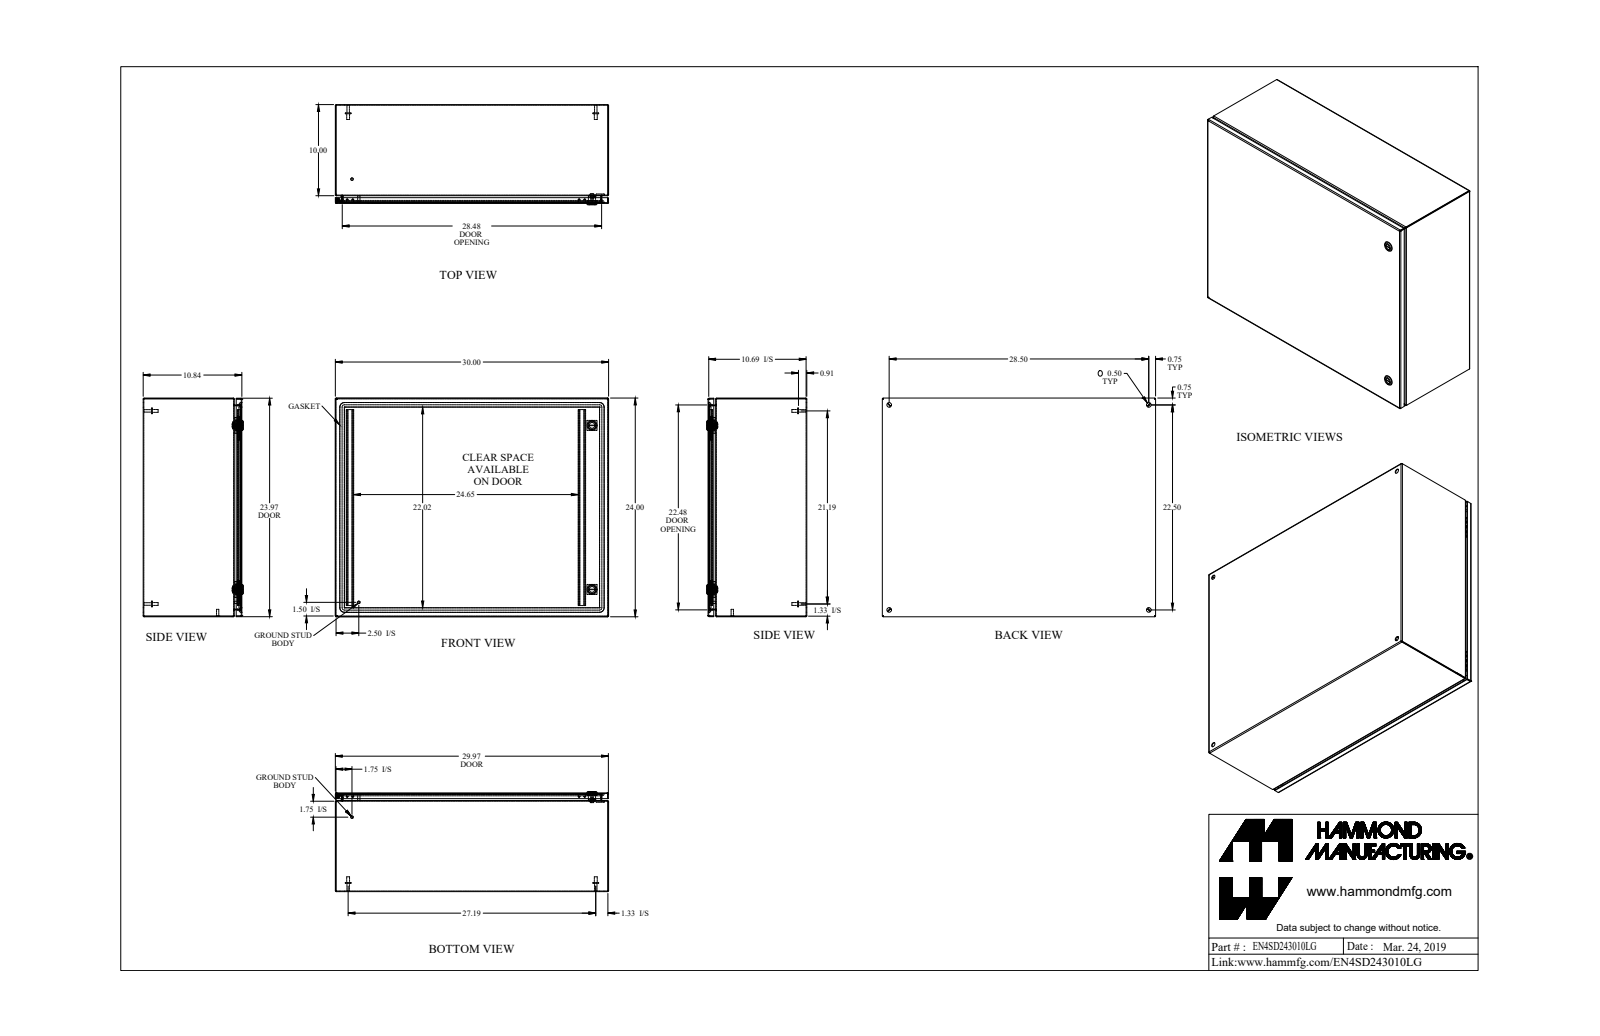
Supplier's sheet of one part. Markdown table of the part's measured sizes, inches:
| quantity | value |
| --- | --- |
| part name | EN4SD243010LG |
| STEP written by | SolidWorks 2019 (AUTOMOTIVE_DESIGN) |
| units | inches |
| bodies | 27 solids, 752 faces (359 planar, 257 cylindrical, 136 other) |
| overall size | 30 × 24 × 10.997 |
| volume | 209.8 in³ |
| surface area | 5 862 in² |
| round holes (diameter × count) | 0.5 × 4, 0.232 × 2, 0.625 × 2, 0.785 × 2, 0.172 × 1, 0.24 × 1, 0.242 × 1 |
| round bosses / shafts (diameter × count) | 0.625 × 4, 0.313 × 4, 0.27 × 4, 1.1 × 2, 0.525 × 2, 0.281 × 2, 0.25 × 2, 0.455 × 1 |
| partial cylindrical surfaces (radius × count) | 0.036 × 16, 0.108 × 16, 0.043 × 12, 0.081 × 12, 0.382 × 12, 0.1 × 8, 19.003 × 8, 0.006 × 4 |
| main face-to-face distances | 0.072, 10.765, 10.693, 10.837, 23.928, 29.928, 23.856, 24, 29.856, 30 |
| hole center spacings | 22.5, 27.519, 28.5, 36.311, 2.493, 2.494, 17.999, 20.277 |
